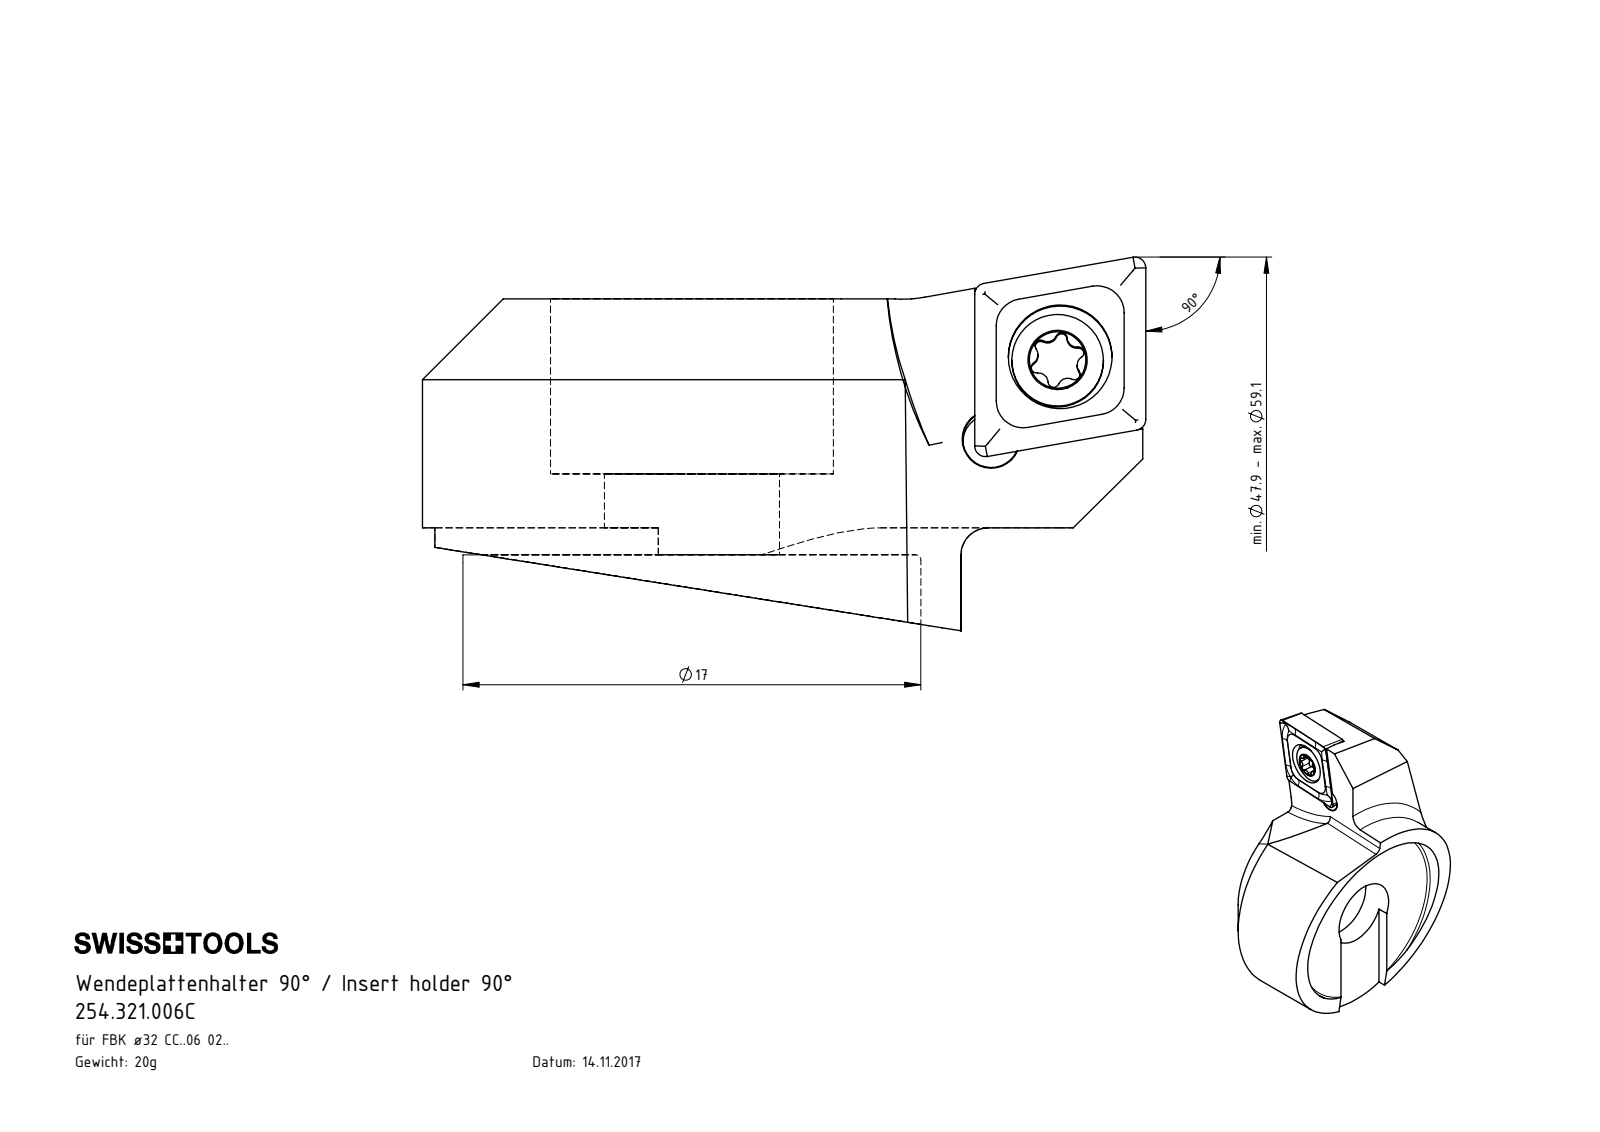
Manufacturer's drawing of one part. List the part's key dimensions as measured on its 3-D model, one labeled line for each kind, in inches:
Part name (STEP PRODUCT): 254.321.006C; WCA-ER2.001.006_A; CCMT060204; F32-WCA.001.011_C_fertigbearbeitet
STEP written by: SolidWorks 2017 (CONFIG_CONTROL_DESIGN)
Units: inches
Bodies: 3 solids, 134 faces (38 planar, 42 cylindrical, 54 other)
Overall size (bounding box): 1.057 × 0.787 × 0.546
Volume: 0.155 in³ · Surface area: 2.968 in²
Round holes (diameter × count): ⌀0.081 ×1, ⌀0.083 ×1, ⌀0.11 ×1, ⌀0.152 ×1, ⌀0.256 ×1, ⌀0.413 ×1
Round bosses / shafts (diameter × count): ⌀0.787 ×1, ⌀0.134 ×1, ⌀0.098 ×1
Partial cylindrical surfaces — rounded edges, fillets, slot ends (radius × count): R0.008 ×6, R0.014 ×5, R0.02 ×2, R0.014 ×1, R0.197 ×1, R0.335 ×1, R0.591 ×1
Main face-to-face distances: 0.039, 0.335, 0.374, 0.256, 0.079, 0.118, 0.09, 0.089, 0.094, 0.094
Hole centre spacings: 0.151, 0.157
